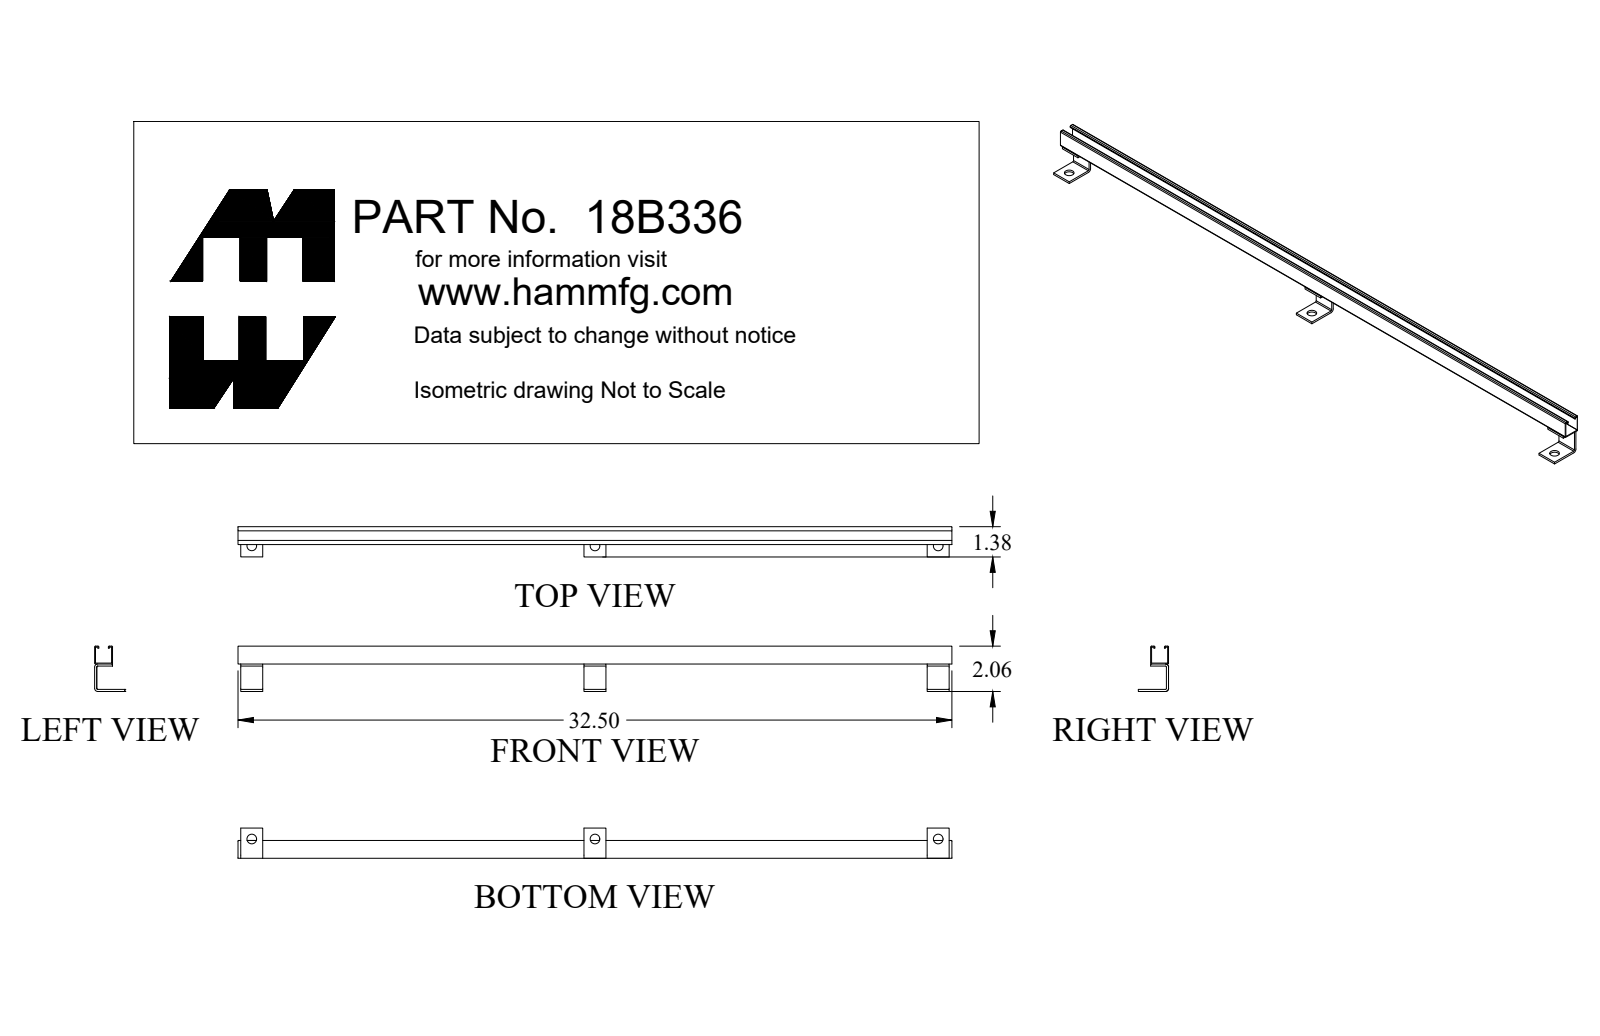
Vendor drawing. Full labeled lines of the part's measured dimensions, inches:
Part name (STEP PRODUCT): 18B336
STEP written by: SolidWorks 2018 (AUTOMOTIVE_DESIGN)
Units: inches
Bodies: 4 solids, 75 faces (48 planar, 27 cylindrical, 0 other)
Overall size (bounding box): 32.5 × 2.063 × 1.376
Volume: 4.374 in³ · Surface area: 199.4 in²
Round holes (diameter × count): ⌀0.437 ×3
Partial cylindrical surfaces — rounded edges, fillets, slot ends (radius × count): R0.043 ×6, R0.048 ×4, R0.143 ×4
Main face-to-face distances: 0.04, 0.773, 0.813, 0.733, 0.773, 0.095, 0.813, 0.733, 0.148, 0.625
Hole centre spacings: 15.625, 31.25
